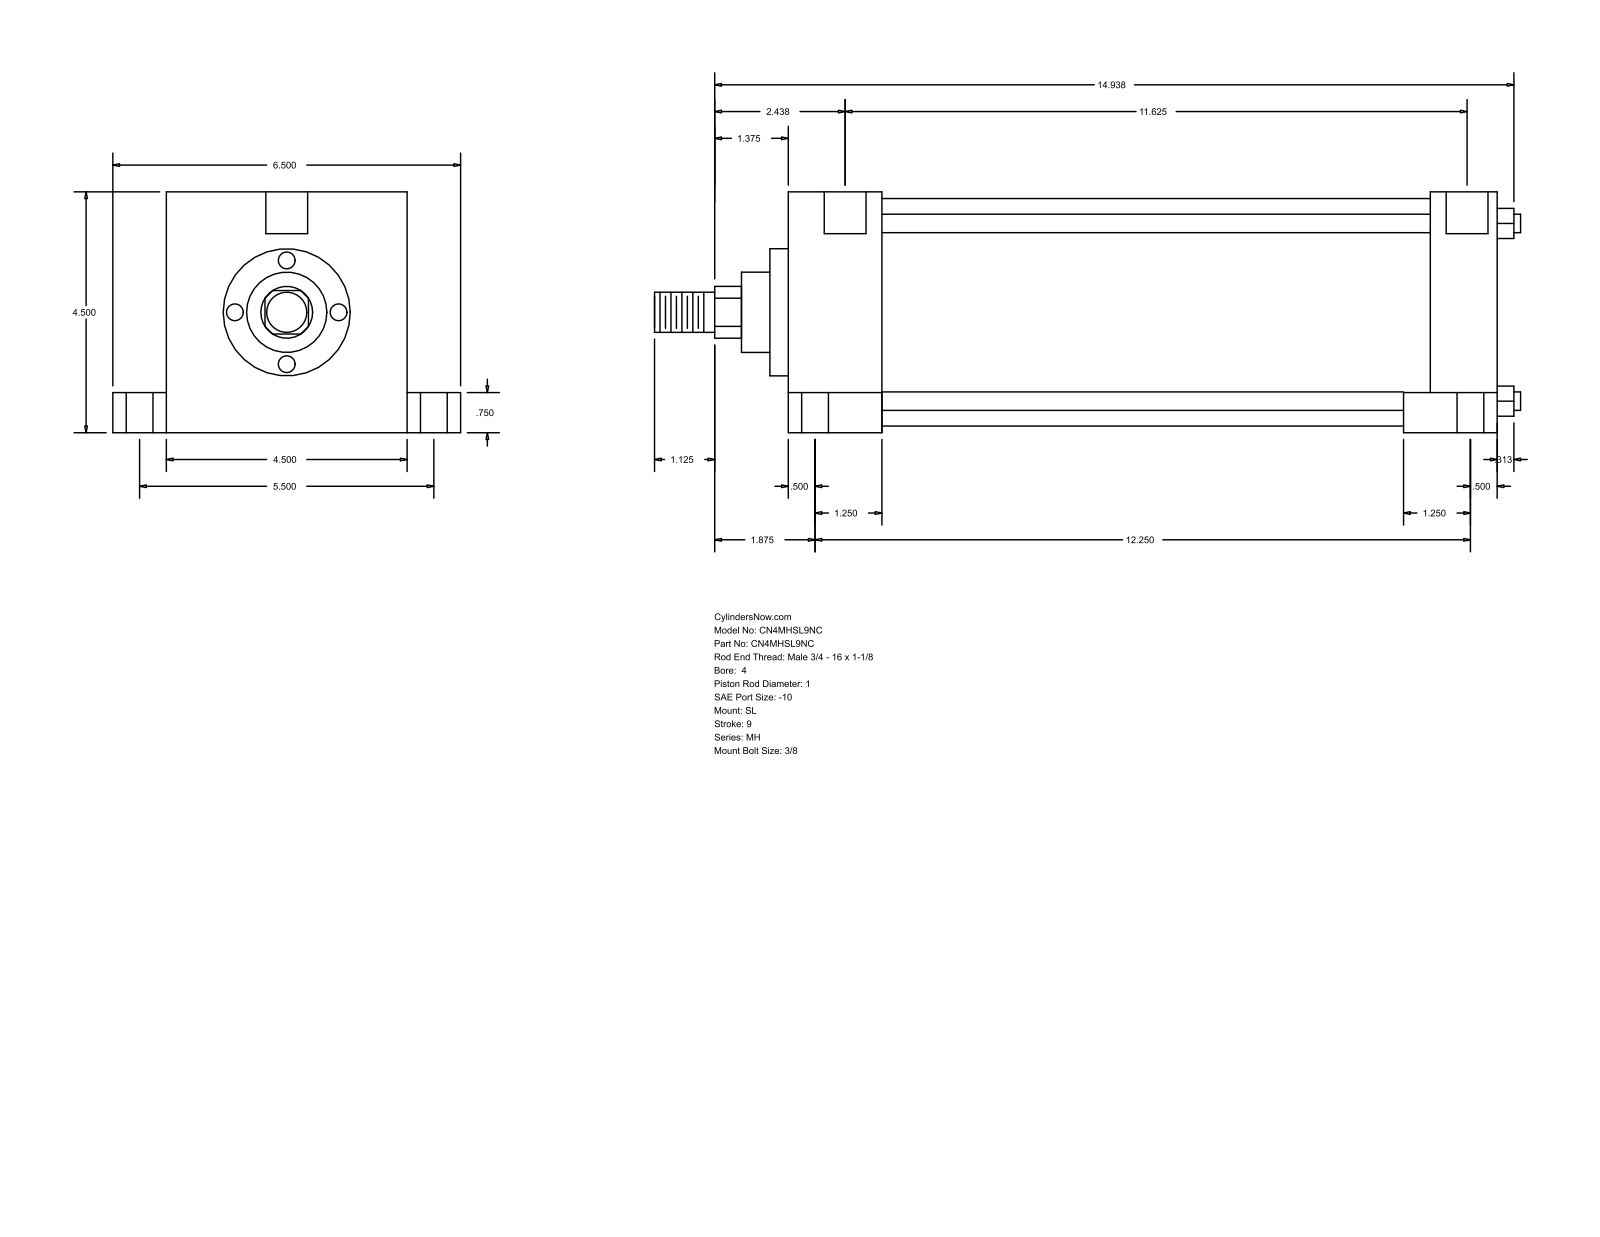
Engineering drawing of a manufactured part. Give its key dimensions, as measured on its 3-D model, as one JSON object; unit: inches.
{"part_name": "MH_SL__0400_1", "step_written_by": "GSSL Pune (CONFIG_CONTROL_DESIGN)", "units": "inches", "bodies": {"solids": 0, "faces": 110, "planar": 77, "cylindrical": 33, "other": 0}, "overall_size": [16.187, 6.5, 4.5], "round_holes": [[0.344, 4], [0.5, 4], [0.75, 4], [0.781, 2]], "round_bosses_or_shafts": [[0.345, 4], [4.25, 1], [2.375, 1], [1.5, 1], [1, 1], [0.75, 1]], "partial_cylinders_radius": [[0.484, 1]], "face_to_face_distances": [4.5, 13.25, 1.75, 11.5, 12, 10.25, 1.25, 1, 5.5, 0.75], "hole_center_spacings": [0.062, 2.75, 2.751, 2.795, 2.807, 5.5, 11.687, 11.75]}
